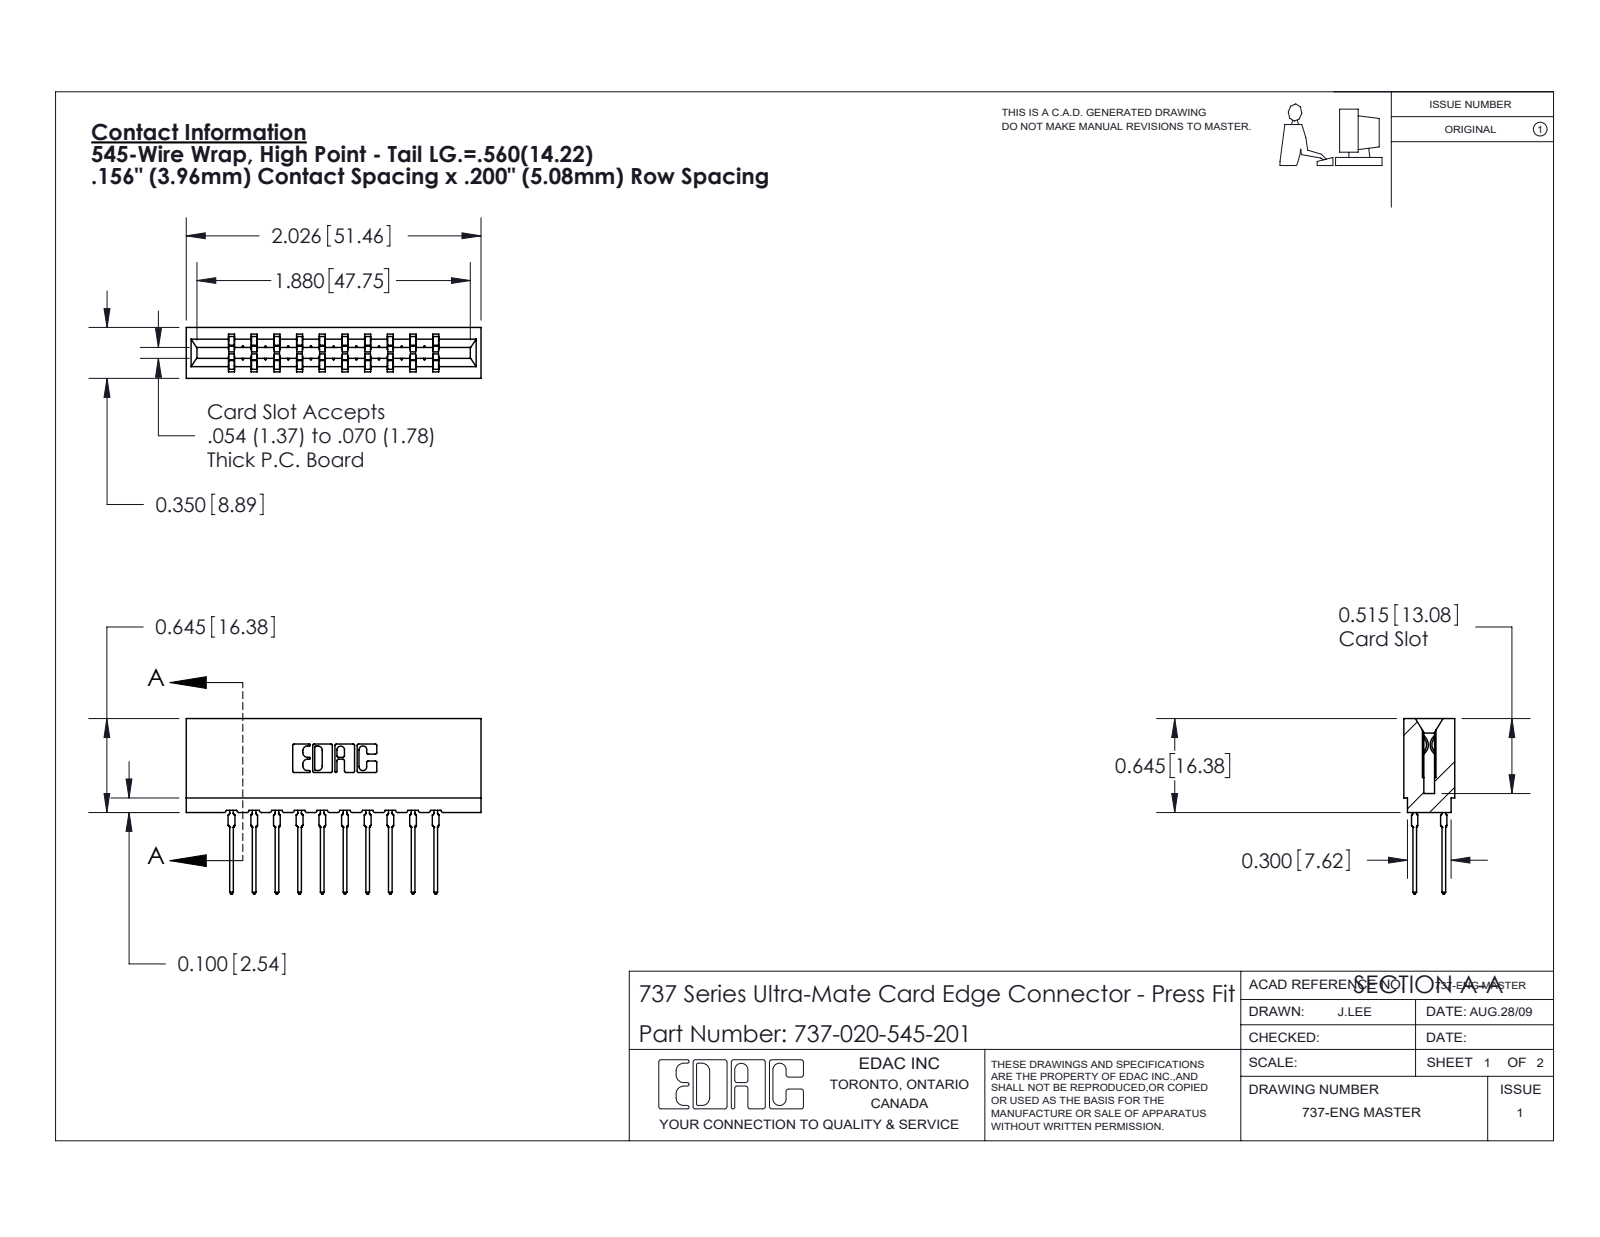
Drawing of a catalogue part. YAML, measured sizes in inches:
part_name: "737-020-545-201; 745-292-001_545; 737 Part_Insulator Option - 01"
step_written_by: "SolidWorks 2020 (CONFIG_CONTROL_DESIGN)"
units: inches
bodies: {solids: 21, faces: 1894, planar: 984, cylindrical: 390, other: 520}
overall_size: [2.026, 1.206, 0.35]
volume: 0.327
surface_area: 11.5
partial_cylinders:
  - {radius: 0.021, count: 40}
  - {radius: 0.01, count: 22}
  - {radius: 0.015, count: 20}
  - {radius: 0.005, count: 8}
  - {radius: 0.011, count: 8}
  - {radius: 0.007, count: 6}
  - {radius: 0.031, count: 6}
  - {radius: 0.026, count: 3}
face_to_face_distances: [0.156, 0.138, 0.212, 0.35, 0.624, 0.312, 0.354, 0.78, 0.468, 0.063]
